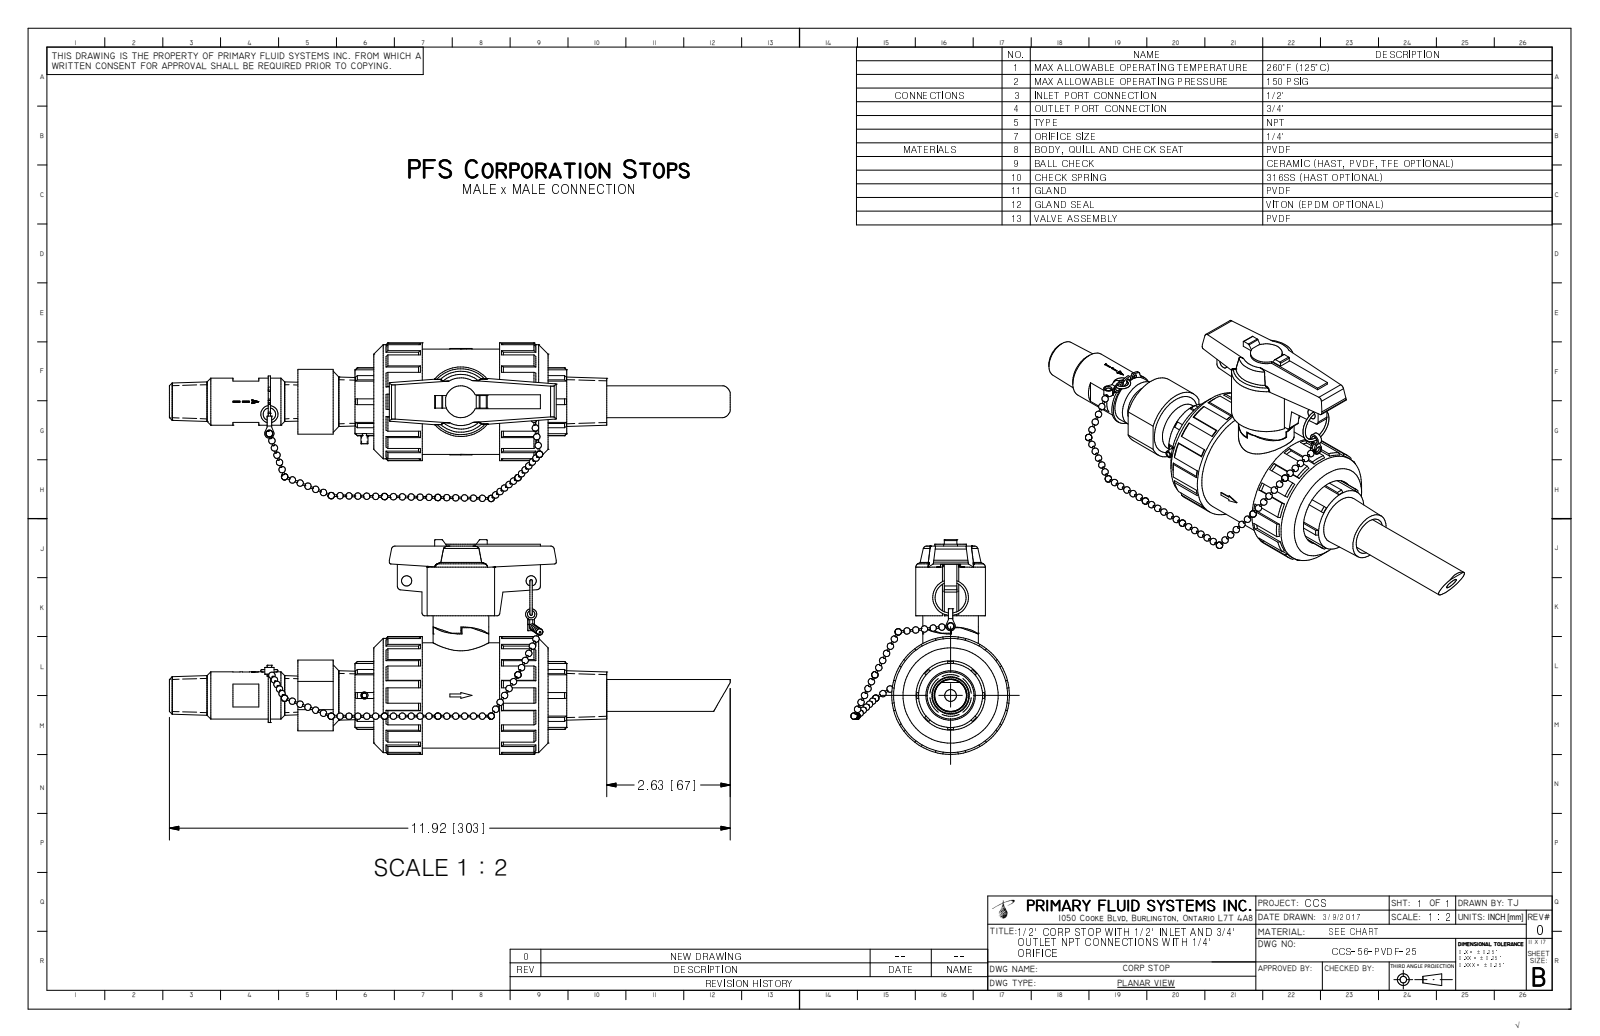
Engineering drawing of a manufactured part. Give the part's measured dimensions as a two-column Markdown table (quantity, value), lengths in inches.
| quantity | value |
| --- | --- |
| part name | CCS-56-PVDF-25_R0 |
| STEP written by | Autodesk Inventor 2009 (AUTOMOTIVE_DESIGN) |
| units | inches |
| bodies | 1 solid, 600 faces (294 planar, 77 cylindrical, 229 other) |
| overall size | 11.922 × 4.554 × 3.369 |
| volume | 25.21 in³ |
| surface area | 117.3 in² |
| round holes (diameter × count) | 0.079 × 1, 0.217 × 1, 0.25 × 1, 0.469 × 1, 0.56 × 1, 1.47 × 1, 2.16 × 1 |
| round bosses / shafts (diameter × count) | 2.5 × 1, 2.422 × 1, 2.232 × 1, 1.801 × 1, 1.476 × 1, 1.36 × 1, 1.181 × 1, 1.18 × 1 |
| partial cylindrical surfaces (radius × count) | 0.02 × 4, 0.079 × 4, 0.039 × 2, 0.043 × 2, 0.059 × 2, 0.157 × 2, 0.337 × 1, 0.463 × 1 |
| main face-to-face distances | 0.039, 0.266, 0.306, 0.472, 3.233, 0.23, 3.475, 0.242, 3.003, 1.03 |
| hole center spacings | 0.535 |
